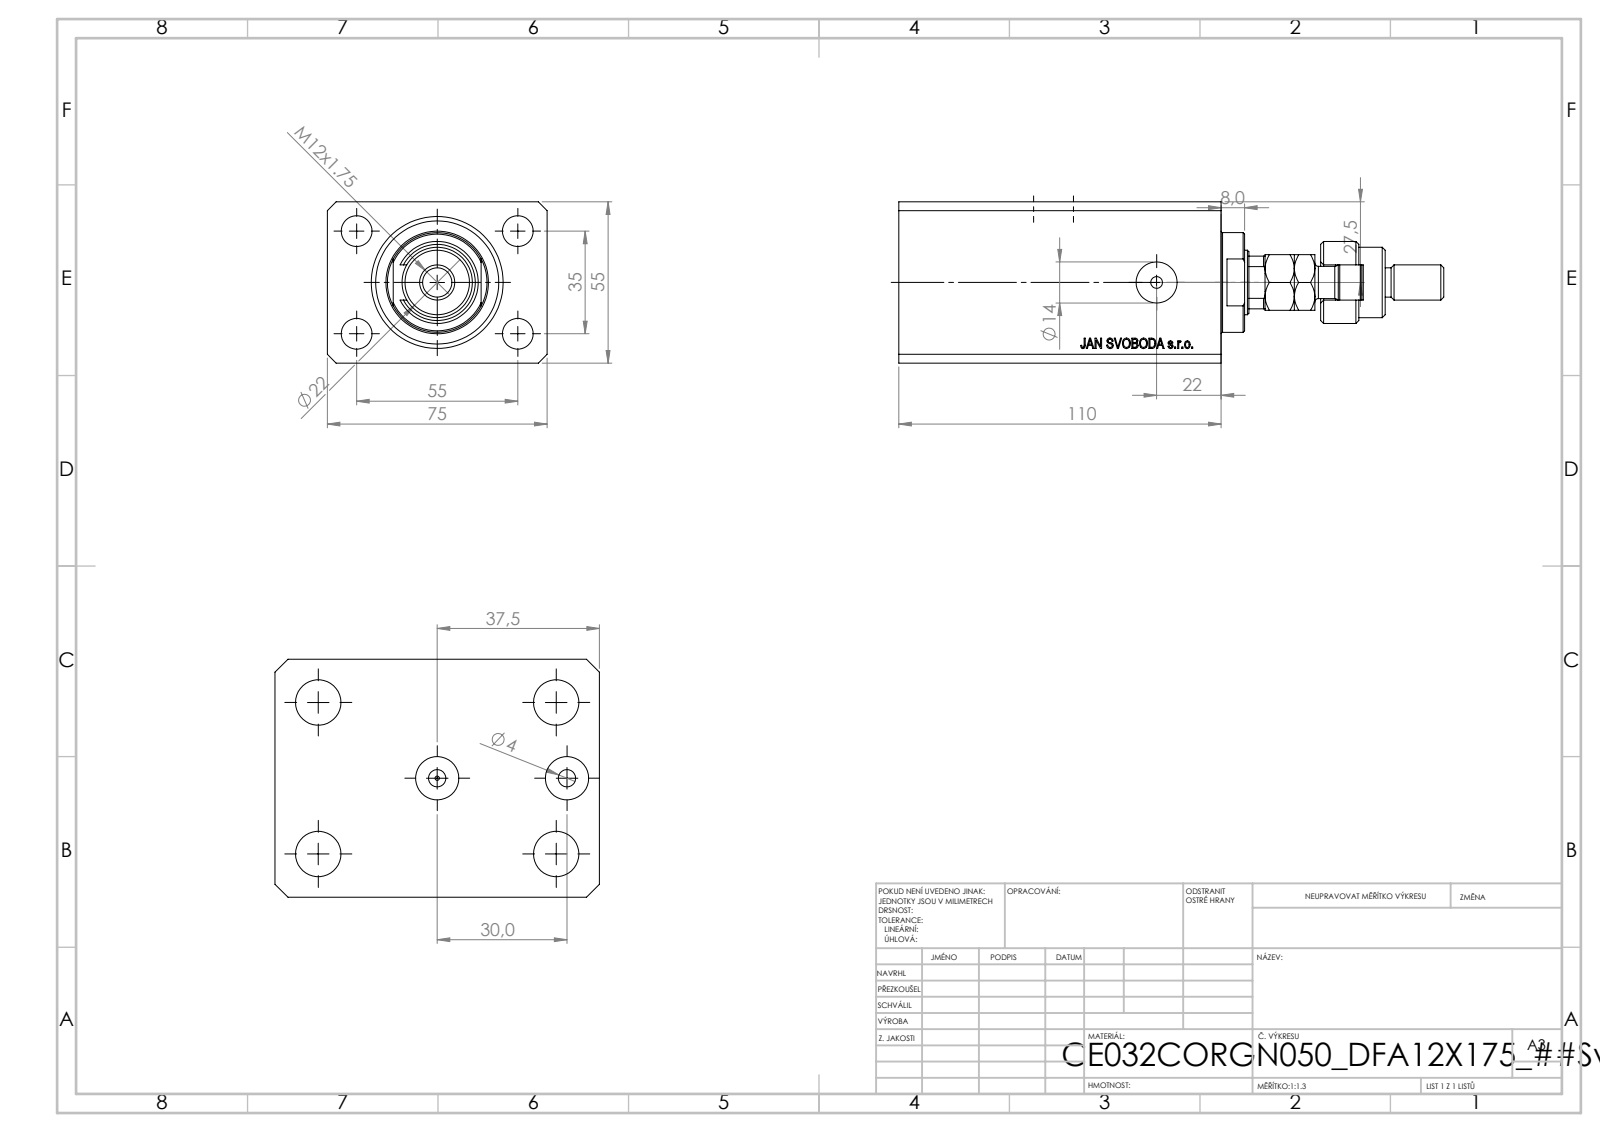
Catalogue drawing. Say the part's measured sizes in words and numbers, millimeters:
The part is named "V250CE_VC_C; V250CE_C_Body; V250CE_C_VCP; MFA (+1 more)". Its 3-D file was written by "SolidWorks 2019 (CONFIG_CONTROL_DESIGN)". It is 5 solids with 953 faces: 456 planar, 59 cylindrical and 438 other. Overall it measures 186 by 75 by 55 millimeters. Its volume is 414 102 cubic millimeters and its surface area 88 476 square millimeters. Round holes: 5 of diameter 10.5, 4 of diameter 4, 2 of diameter 10, 2 of diameter 14, 1 of diameter 1.25, 1 of diameter 22, 1 of diameter 32, 1 of diameter 45. Round bosses or shafts: 1 of diameter 34, 1 of diameter 28, 1 of diameter 24, 1 of diameter 18, 1 of diameter 12, 1 of diameter 11. Partial cylindrical surfaces (rounded edges, fillets, slot ends): 1 of radius 9.75, 1 of radius 10.5. The main face-to-face distances are 55, 75, 15, 110, 95, 9.9, 85.1, 100.1, 8, 87.66. The hole center spacings are 32.6, 17.68, 35, 55, 60.1, 65.19, 30, 66.
